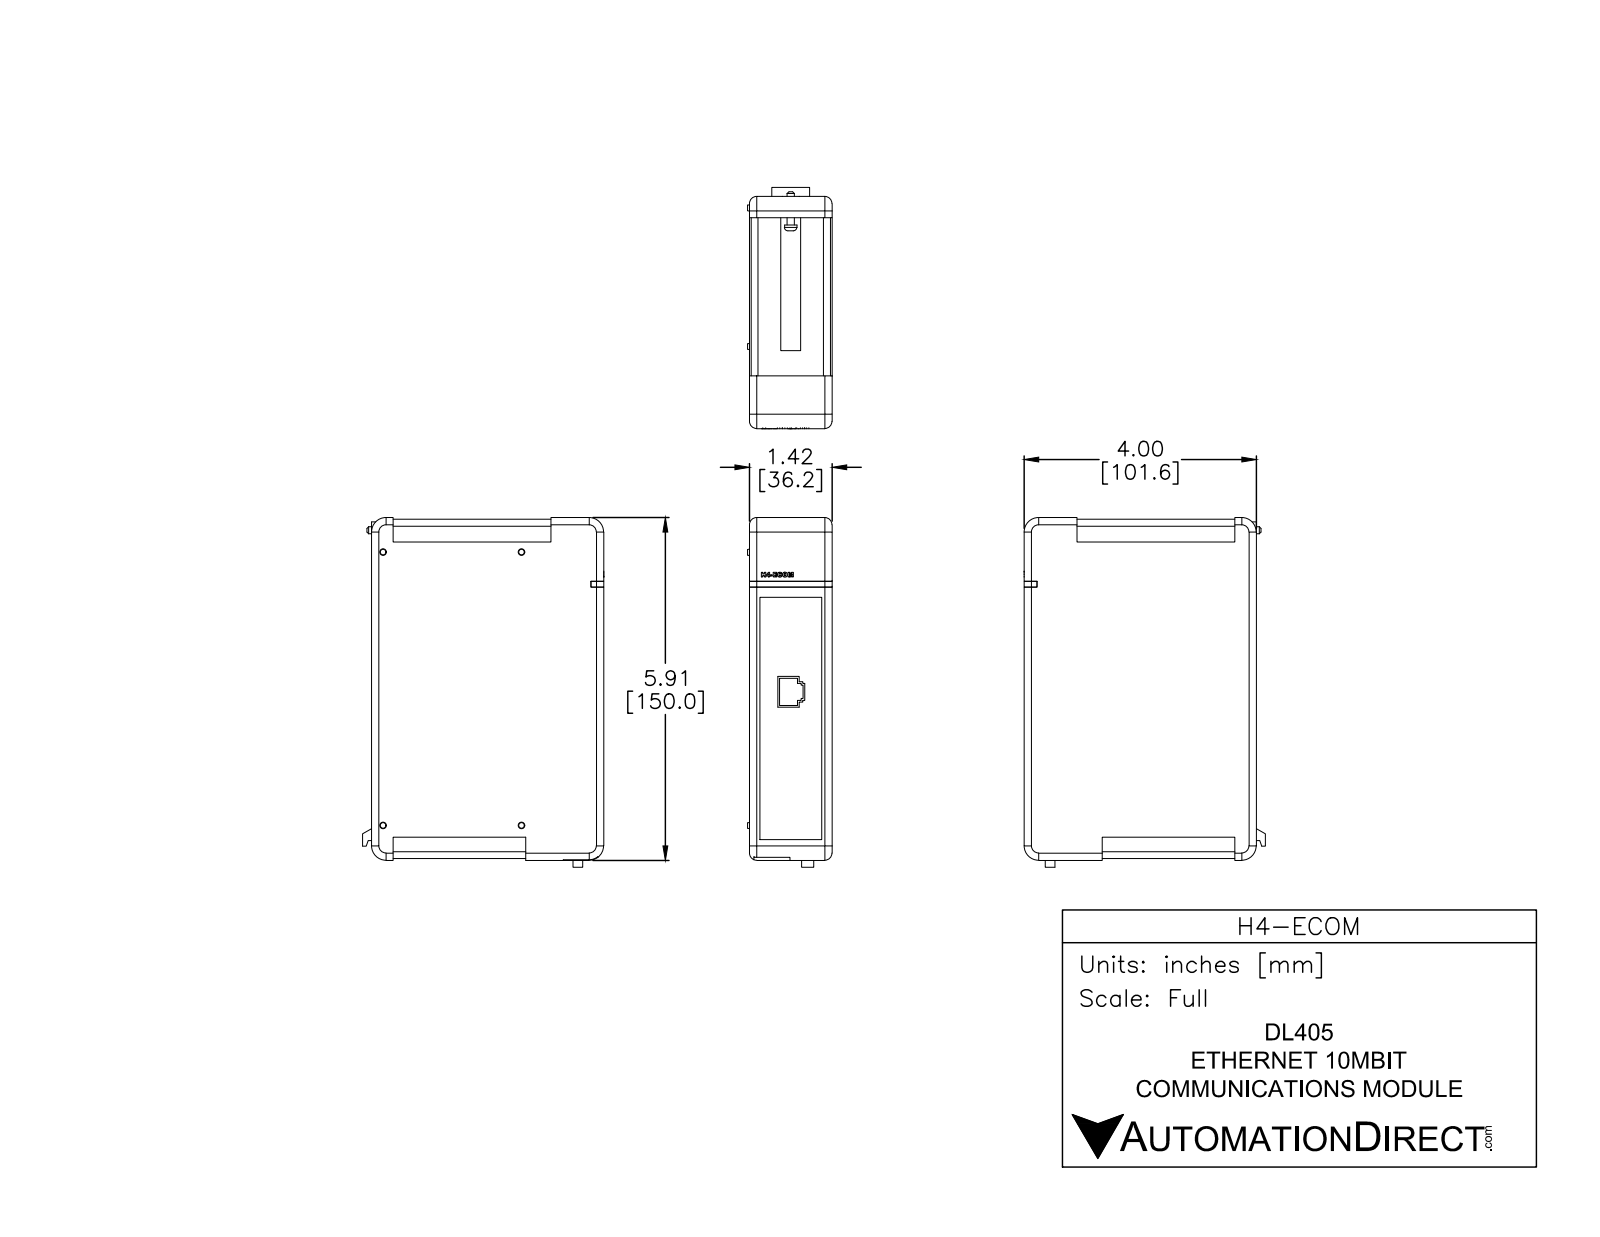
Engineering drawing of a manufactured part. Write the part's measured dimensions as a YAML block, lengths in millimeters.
part_name: "H4-ECOM"
step_written_by: "SolidWorks 2014 (AUTOMOTIVE_DESIGN)"
units: millimeters
bodies: {solids: 2, faces: 261, planar: 185, cylindrical: 34, other: 42}
overall_size: [153, 105.6, 37]
volume: 525900
surface_area: 52430
round_bosses_or_shafts:
  - {diameter: 5.4, count: 1}
  - {diameter: 3.1, count: 1}
partial_cylinders:
  - {radius: 3.2, count: 8}
  - {radius: 3, count: 4}
  - {radius: 6.4, count: 4}
  - {radius: 3.7, count: 1}
  - {radius: 4.3, count: 1}
face_to_face_distances: [36.2, 0.8, 100.8, 35.4, 148.5, 149.2, 101.6, 5.1, 95.8, 96.5]
